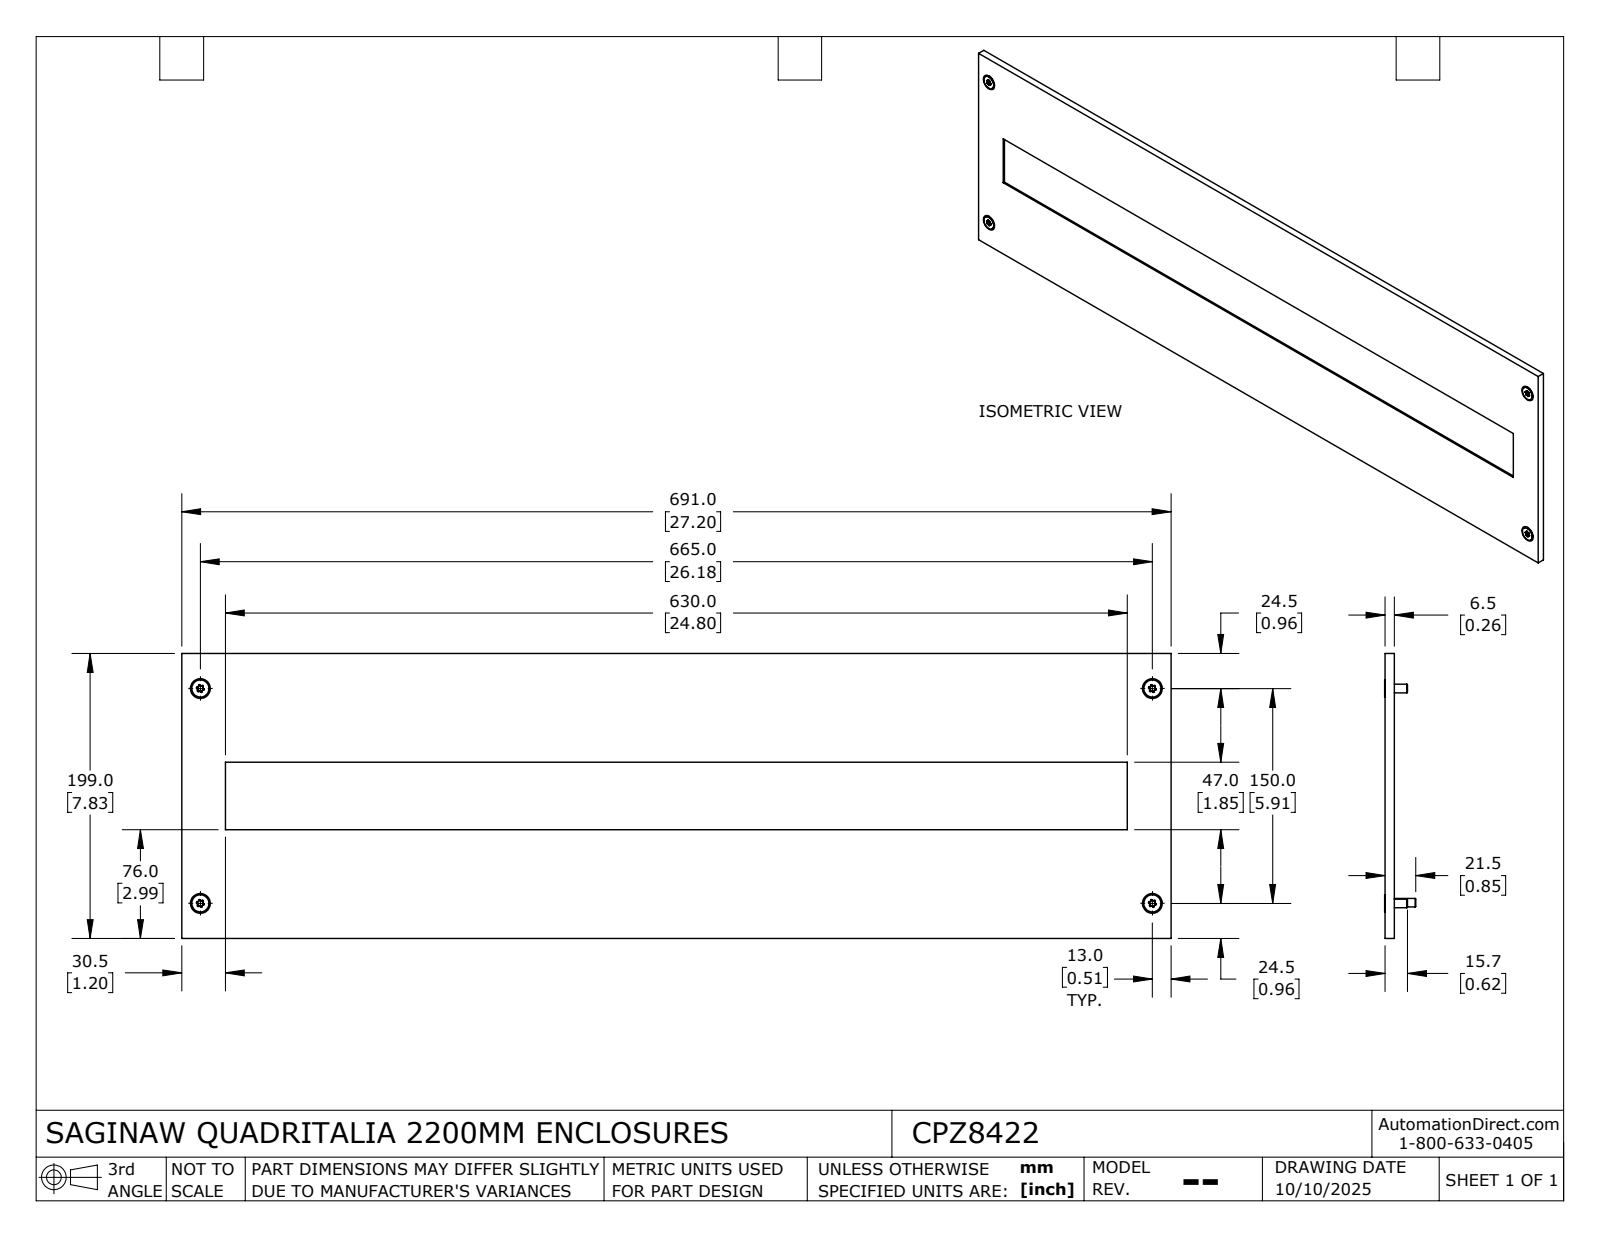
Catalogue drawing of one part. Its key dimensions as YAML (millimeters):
part_name: "CPZ8422_Default; CPZ8422"
step_written_by: "SolidWorks 2024 (CONFIG_CONTROL_DESIGN)"
units: millimeters
bodies: {solids: 1, faces: 176, planar: 81, cylindrical: 66, other: 29}
overall_size: [691, 199, 21.8]
volume: 177630
surface_area: 240091
round_holes:
  - {diameter: 3.96, count: 4}
round_bosses_or_shafts:
  - {diameter: 6, count: 5}
  - {diameter: 12, count: 4}
  - {diameter: 7, count: 1}
partial_cylinders:
  - {radius: 0.5, count: 48}
face_to_face_distances: [1.5, 197.5, 199, 196, 6.5, 5, 689.5, 76, 123, 74.5]
hole_center_spacings: [150, 665, 681.71]
